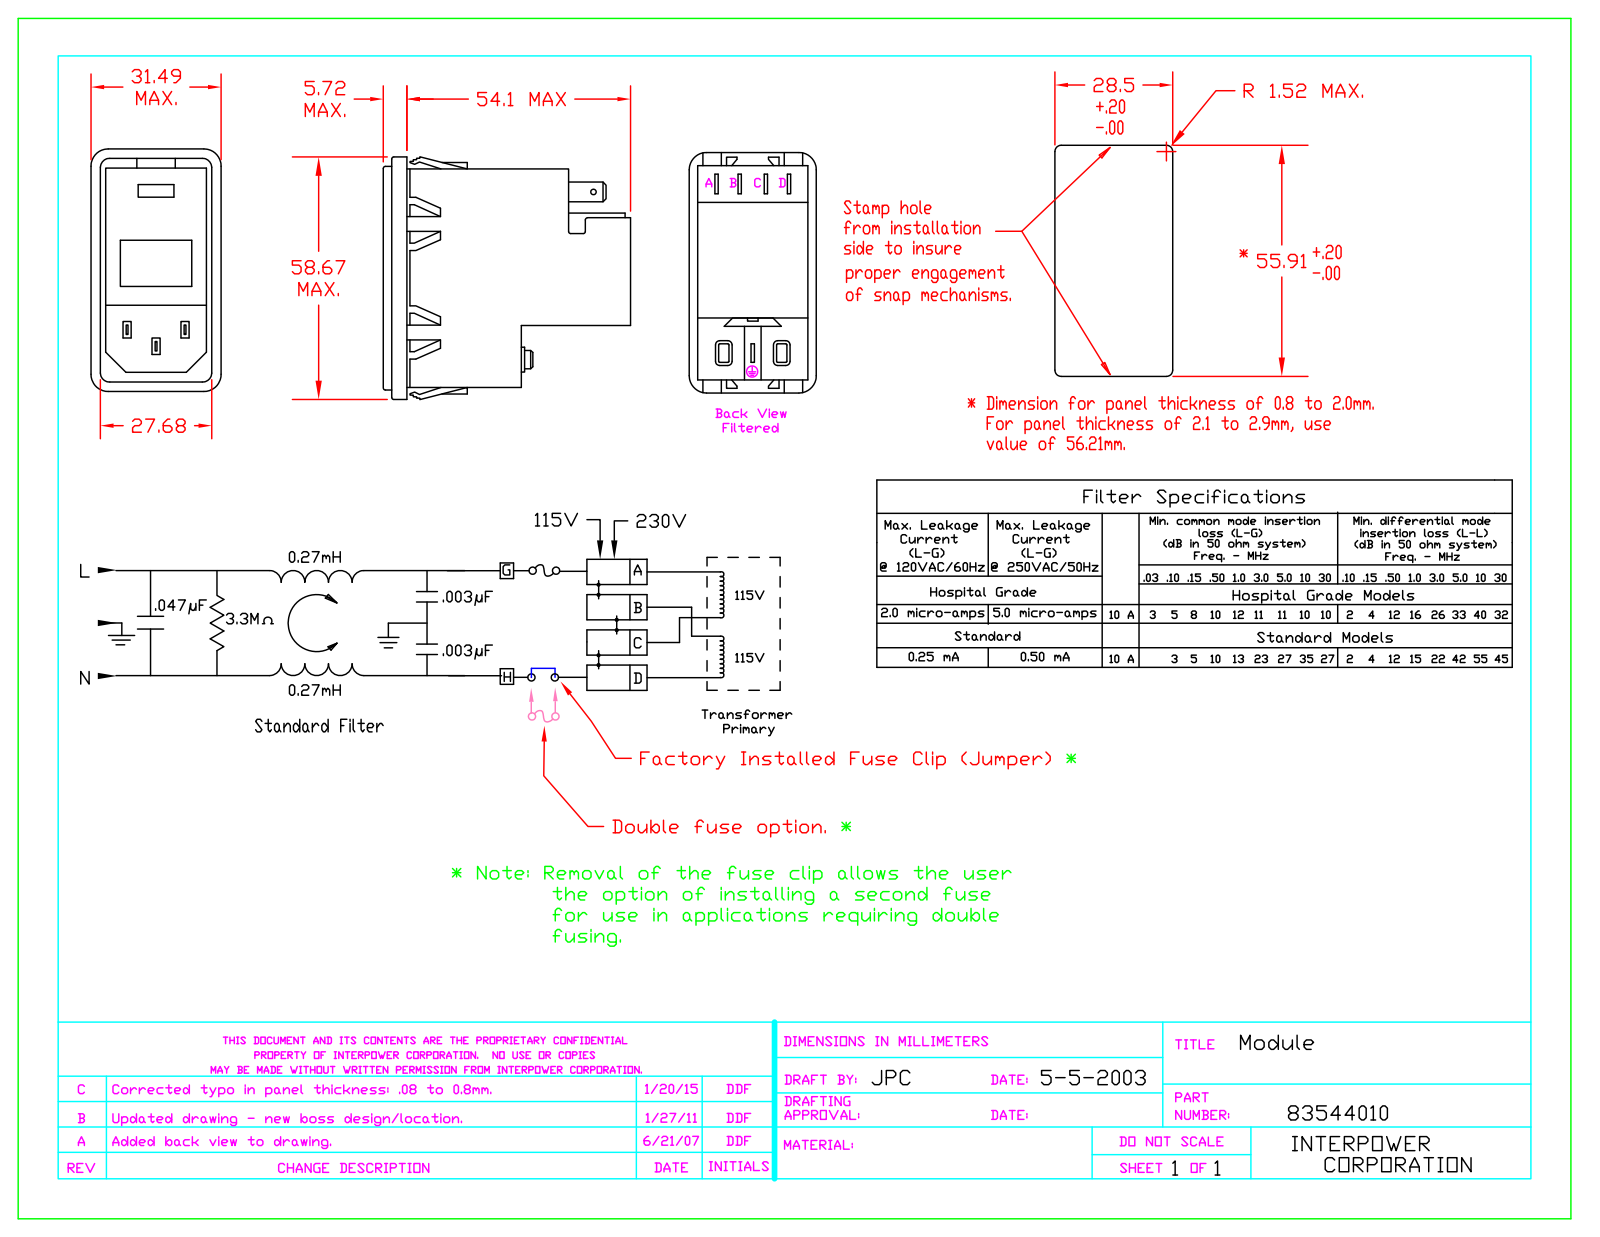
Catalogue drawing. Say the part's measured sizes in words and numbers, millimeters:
The part is named "83544010-R1". Its 3-D file was written by "SolidWorks 2007 (CONFIG_CONTROL_DESIGN)". It is 2 solids with 885 faces: 697 planar, 128 cylindrical and 60 other. Overall it measures 60.27 by 59.52 by 31.49 millimeters. Its volume is 64 172 cubic millimeters and its surface area 35 799 square millimeters. Round holes: 1 of diameter 1.33. Partial cylindrical surfaces (rounded edges, fillets, slot ends): 30 of radius 1, 15 of radius 0.25, 15 of radius 0.7, 8 of radius 0.51, 8 of radius 0.6, 8 of radius 0.74, 8 of radius 1.5, 8 of radius 1.75. The main face-to-face distances are 0.45, 0.87, 0.42, 26.42, 26.87, 27.29, 26, 26.84, 27.74, 0.76.
